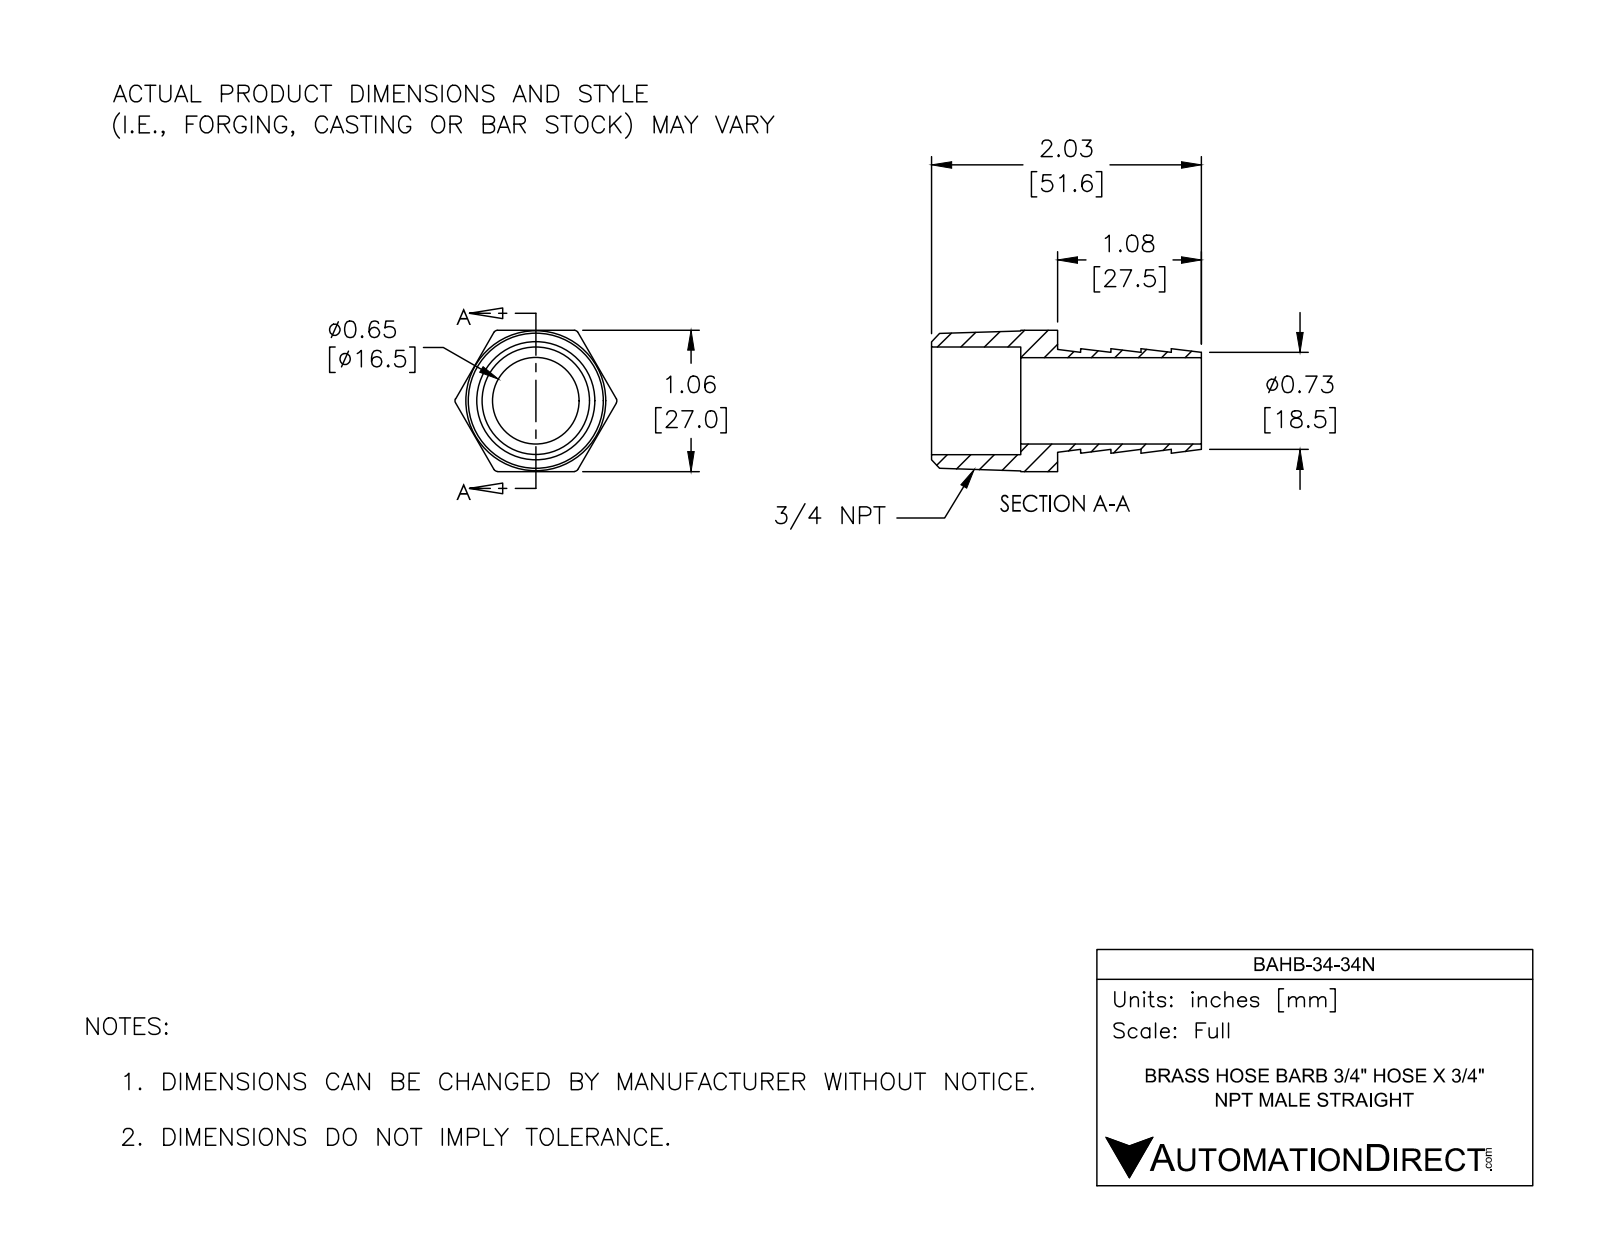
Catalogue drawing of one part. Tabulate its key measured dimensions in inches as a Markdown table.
| quantity | value |
| --- | --- |
| part name | BAHB-34-34N |
| STEP written by | SolidWorks 2017 (AUTOMOTIVE_DESIGN) |
| units | inches |
| bodies | 1 solid, 39 faces (15 planar, 10 cylindrical, 14 other) |
| overall size | 2.03 × 1.218 × 1.063 |
| volume | 0.517 in³ |
| surface area | 11.6 in² |
| round holes (diameter × count) | 0.65 × 1, 0.81 × 1 |
| partial cylindrical surfaces (radius × count) | 0.03 × 6 |
| main face-to-face distances | 1.062, 0.277, 0.454, 0.227, 0.227, 0.948, 0.671, 1.082, 1.359, 2.03 |
